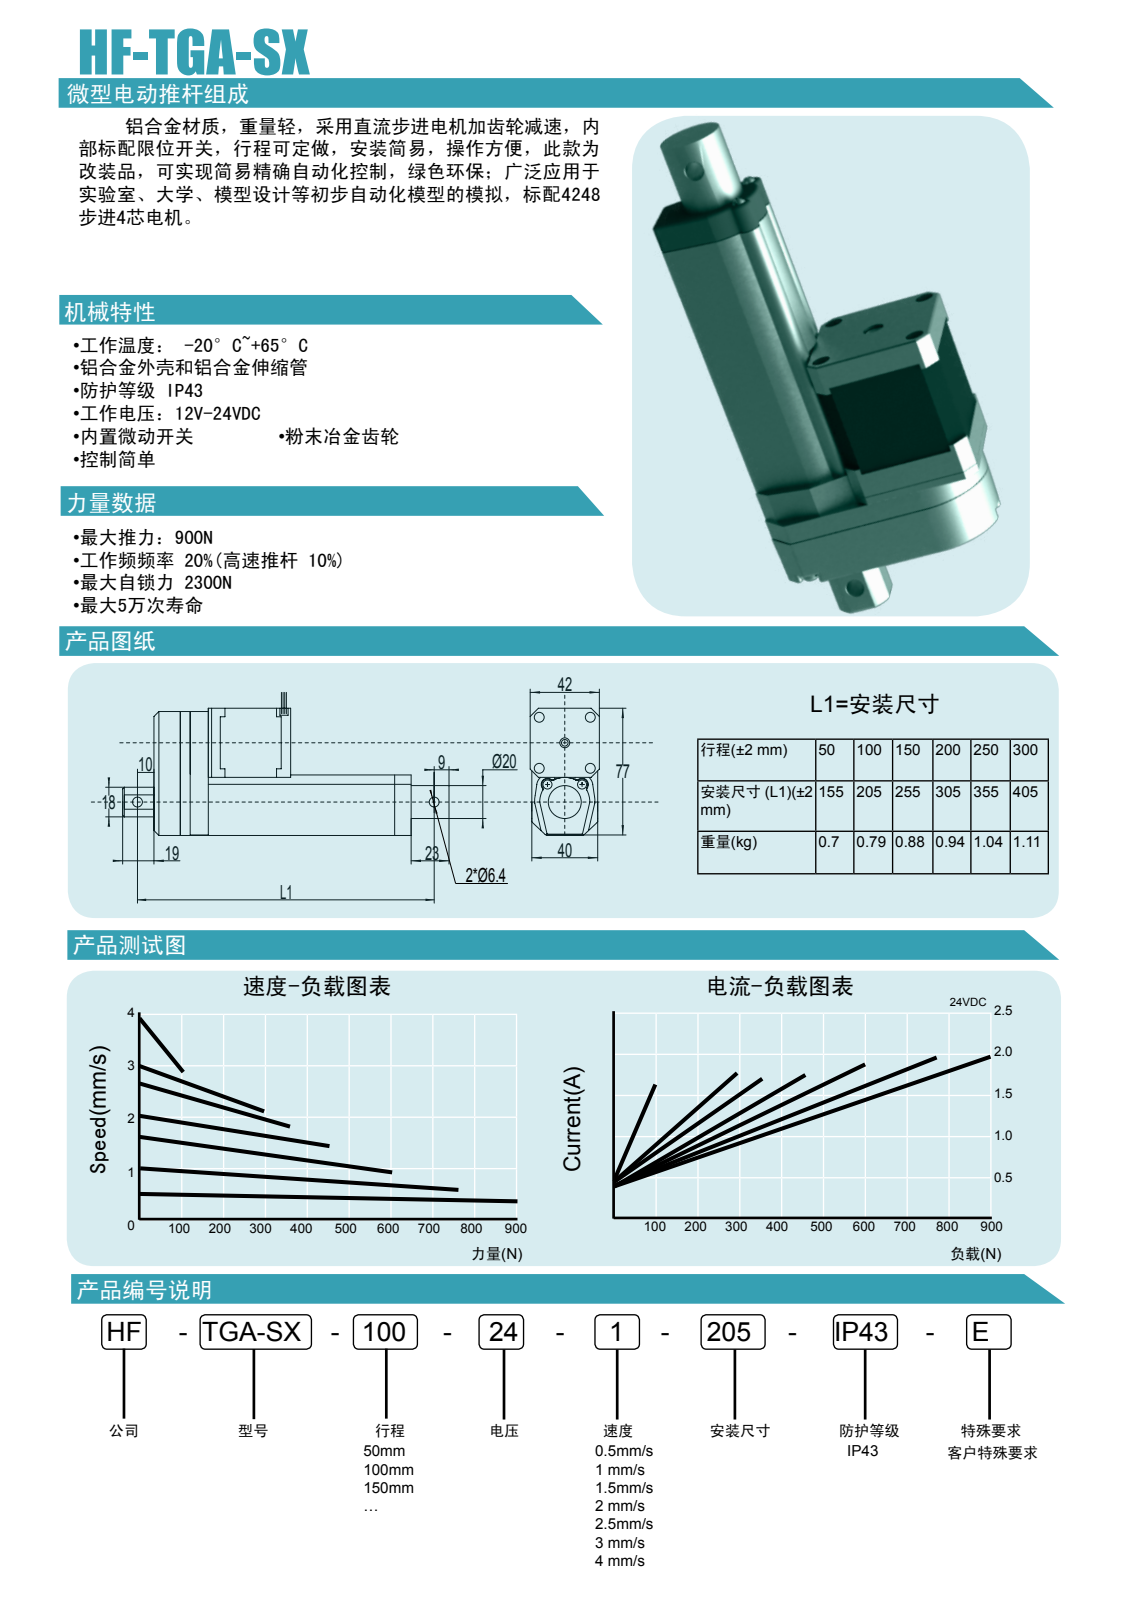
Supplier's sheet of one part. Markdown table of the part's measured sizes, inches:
| quantity | value |
| --- | --- |
| part name | TGA-A-UP_AF0; END; TGA-A-WAIKE_AF0; TGA-A-FENGTOU (+3 more) |
| STEP written by | PRO/ENGINEER BY PARAMETRIC TECHNOLOGY CORPORATION, 2008380 (CONFIG_CONTROL_DESIGN) |
| units | inches |
| bodies | 7 solids, 405 faces (221 planar, 94 cylindrical, 90 other) |
| overall size | 8.78 × 2.992 × 1.654 |
| volume | 21.6 in³ |
| surface area | 104.6 in² |
| round holes (diameter × count) | 0.236 × 6, 0.276 × 1, 0.787 × 1 |
| round bosses / shafts (diameter × count) | 0.236 × 4 |
| partial cylindrical surfaces (radius × count) | 0.039 × 19, 0.02 × 9, 0.157 × 5, 0.02 × 4, 0.071 × 4, 0.138 × 2, 0.394 × 1, 0.587 × 1 |
| main face-to-face distances | 0.26, 1.654, 0.02, 0.902, 0.642, 0.433, 0.118, 1.575, 1.02, 0.378 |
| hole center spacings | 0.891, 1.26, 0.975, 1.781, 2.101, 1.374, 8.071 |
